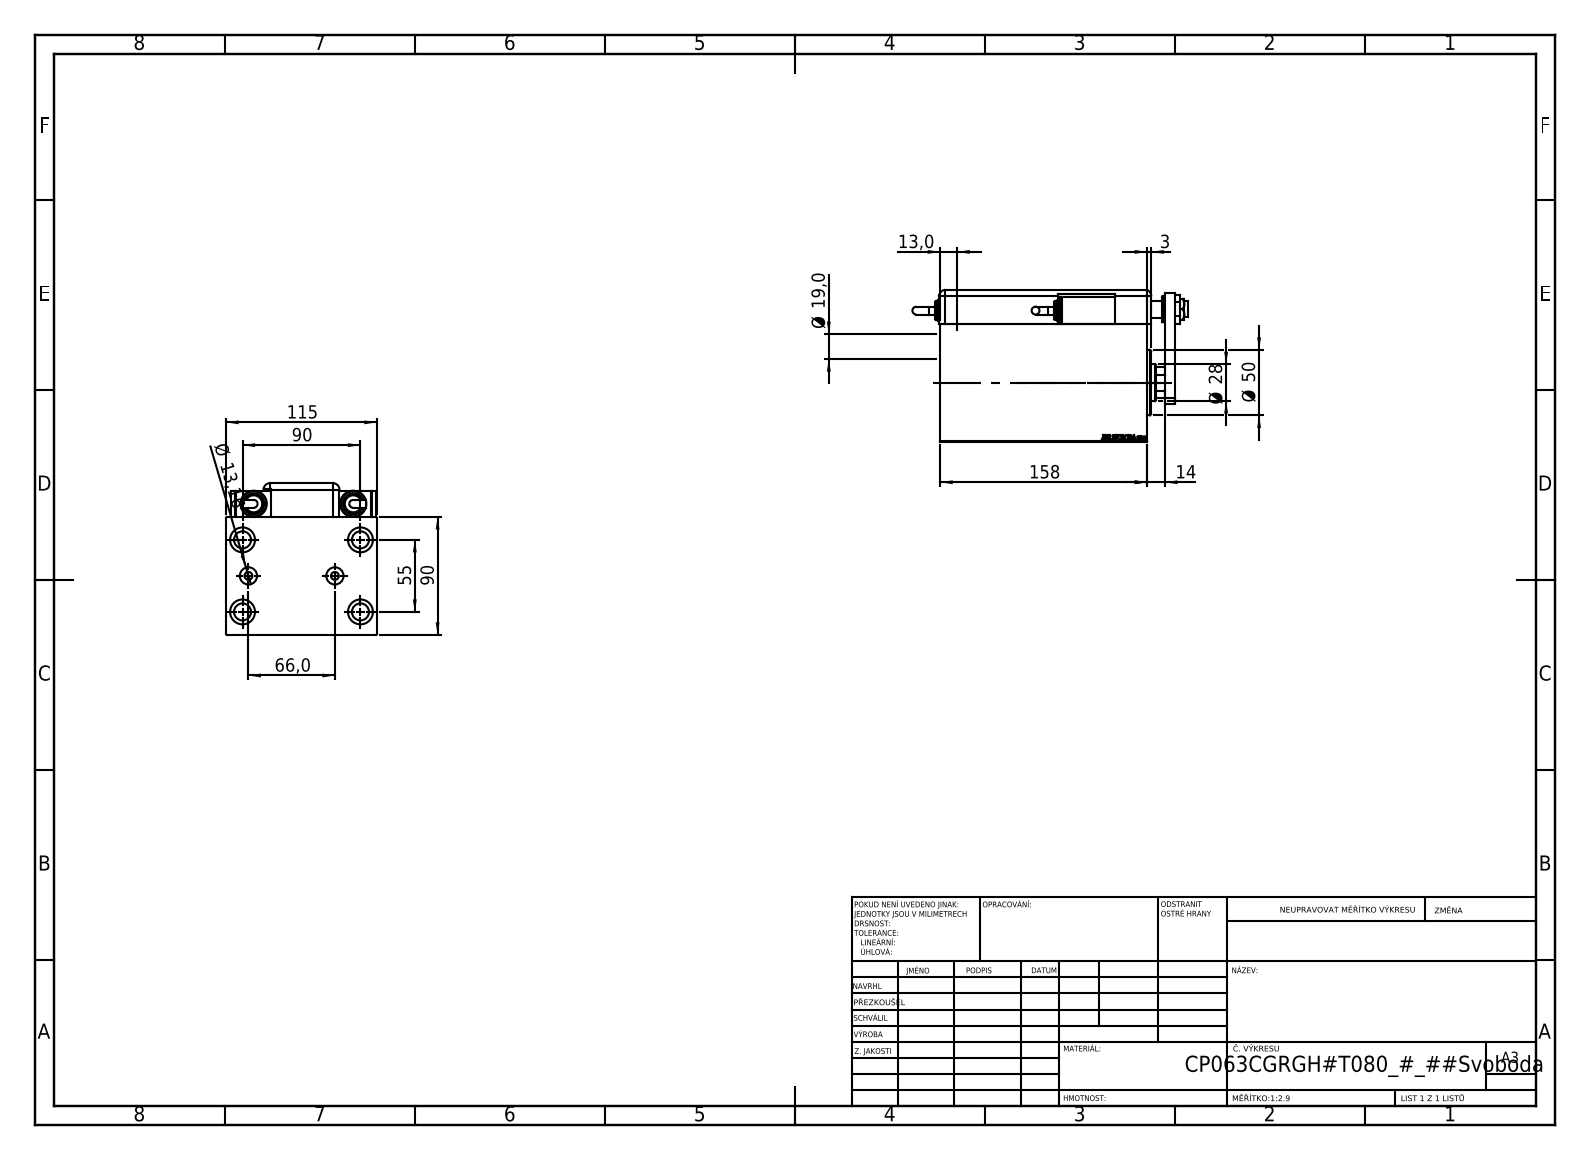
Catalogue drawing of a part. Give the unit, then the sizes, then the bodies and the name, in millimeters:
Units: millimetres
Overall size (bounding box): 210.46 × 115.8 × 115
Round holes (diameter × count): ⌀13 ×5, ⌀19 ×4, ⌀4 ×2, ⌀6 ×2, ⌀8 ×2, ⌀13.16 ×2, ⌀12 ×1, ⌀14 ×1, ⌀18.5 ×1, ⌀20 ×1, ⌀28 ×1, ⌀31.5 ×1
Round bosses / shafts (diameter × count): ⌀20 ×3, ⌀16 ×2, ⌀14 ×2, ⌀6 ×2, ⌀50 ×1
Partial cylindrical surfaces — rounded edges, fillets, slot ends (radius × count): R5 ×9, R10 ×1, R13.5 ×1
Main face-to-face distances: 90, 115, 3, 158, 25.8, 115.8, 17.5, 140.5, 28.5, 112.8
Hole centre spacings: 52.74, 53.27, 27.87, 33.71, 52.22, 55, 75.67, 89.81
Volume: 1 504 000 mm³ · Surface area: 251 434 mm²
Bodies: 13 solids, 1244 faces (614 planar, 113 cylindrical, 517 other)
Part name (STEP PRODUCT): KRYT; V450CM_VC_B; NUT_D19; ZARAZKA_Q (+7 more)
STEP written by: SolidWorks 2019 (CONFIG_CONTROL_DESIGN)
